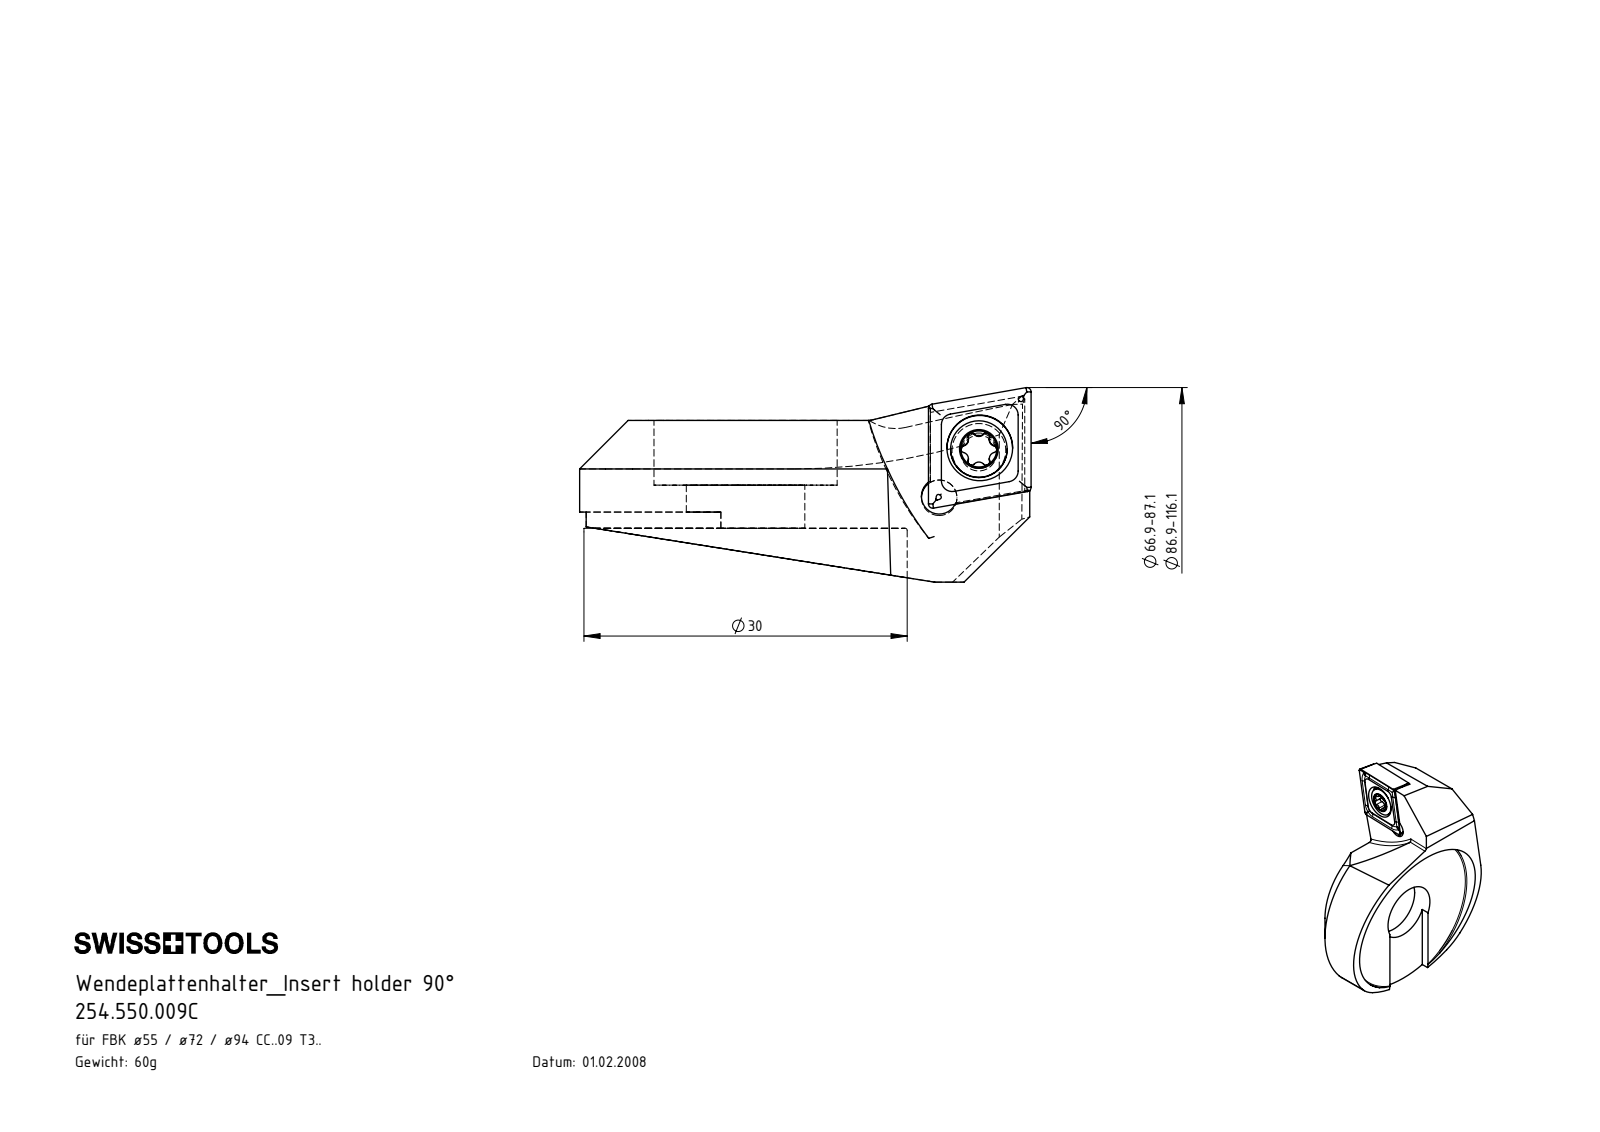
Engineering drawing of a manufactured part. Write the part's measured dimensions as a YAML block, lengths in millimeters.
part_name: "WCA-ER2.001.005_A; F55-WCA.001.013_D_fertigbearbeitet; 254.550.009C; CCMT060204"
step_written_by: "SolidWorks 2017 (CONFIG_CONTROL_DESIGN)"
units: millimeters
bodies: {solids: 5, faces: 153, planar: 48, cylindrical: 48, other: 57}
overall_size: [41.9, 33.1, 18.05]
volume: 8032
surface_area: 4569
round_holes:
  - {diameter: 2.05, count: 1}
  - {diameter: 2.1, count: 1}
  - {diameter: 2.8, count: 1}
  - {diameter: 3.85, count: 1}
  - {diameter: 11, count: 1}
  - {diameter: 17, count: 1}
  - {diameter: 30, count: 1}
round_bosses_or_shafts:
  - {diameter: 3.4, count: 1}
  - {diameter: 2.5, count: 1}
partial_cylinders:
  - {radius: 0.21, count: 6}
  - {radius: 0.36, count: 5}
  - {radius: 0.5, count: 2}
  - {radius: 10, count: 2}
  - {radius: 0.36, count: 1}
  - {radius: 1.05, count: 1}
  - {radius: 5, count: 1}
  - {radius: 16.55, count: 1}
face_to_face_distances: [10, 9, 1, 5, 6, 4, 8.5, 7.5, 2.5, 1.5]
hole_center_spacings: [3.91, 4.04]
